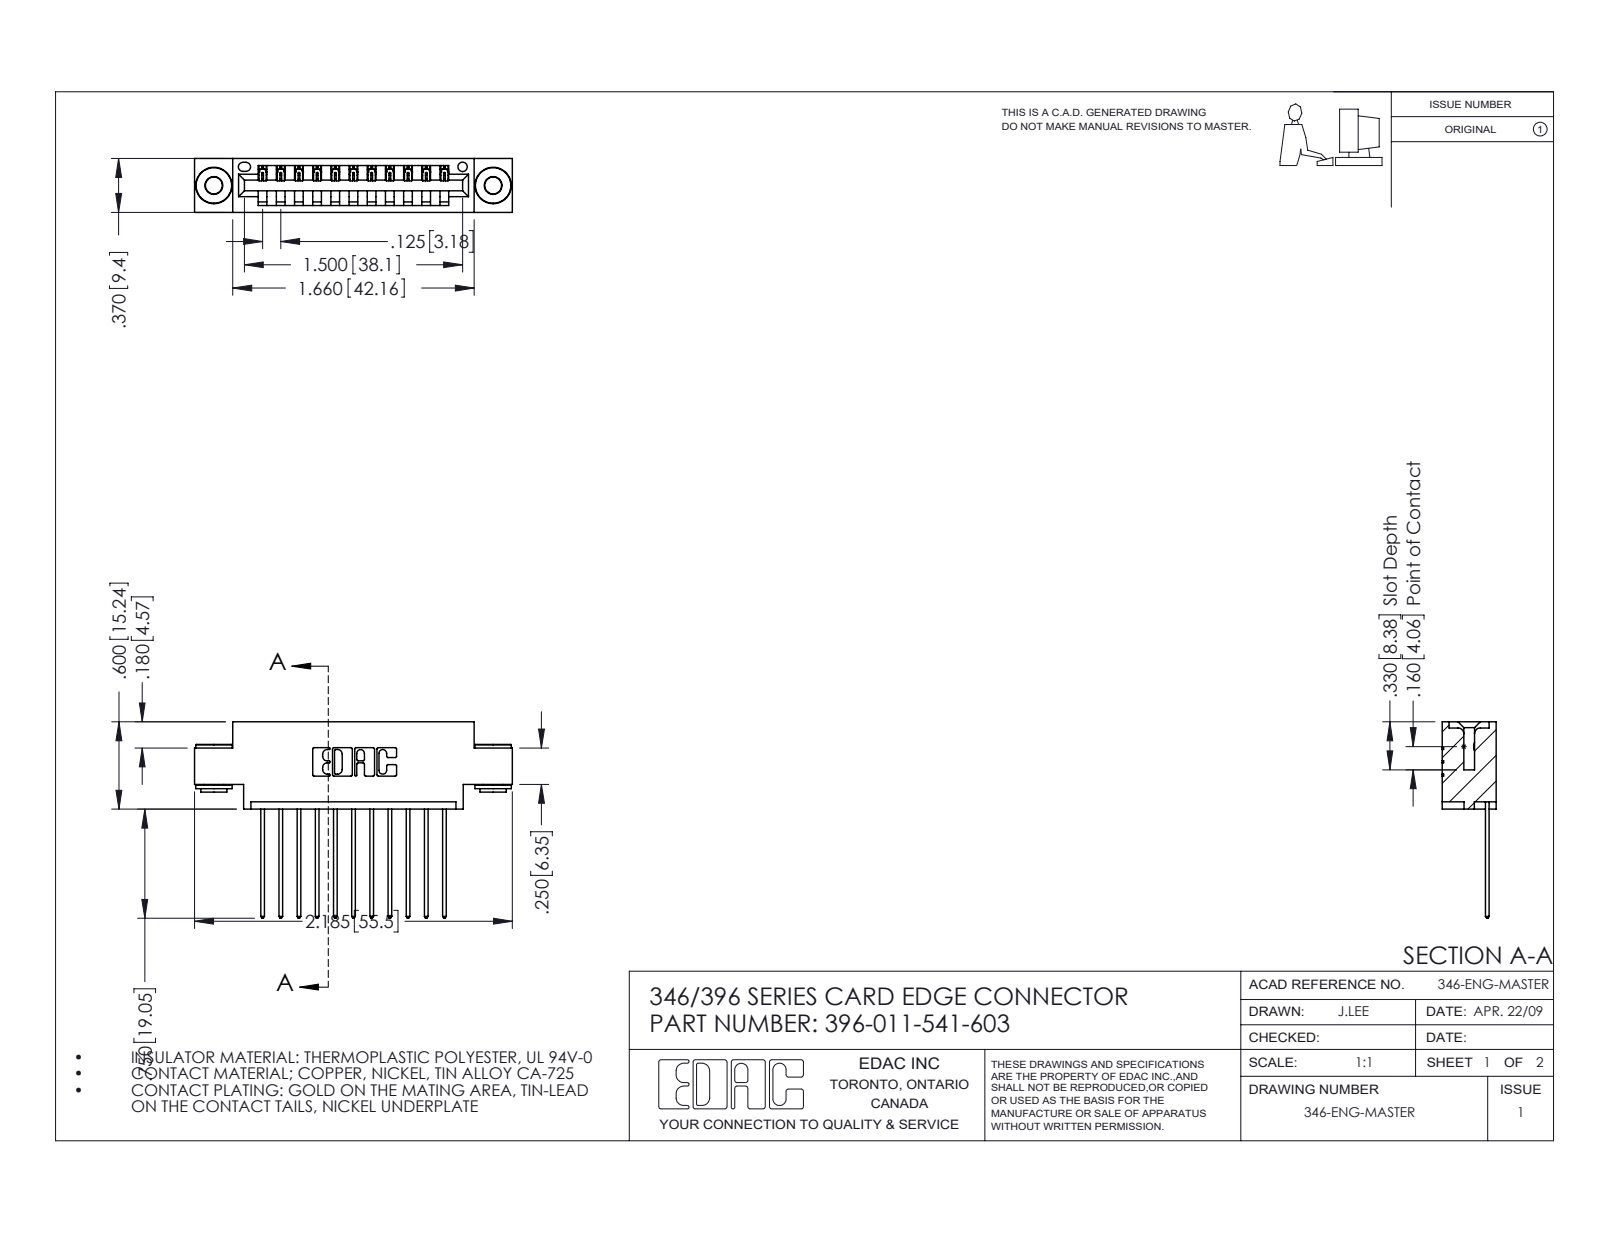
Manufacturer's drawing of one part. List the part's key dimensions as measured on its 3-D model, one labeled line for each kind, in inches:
Part name (STEP PRODUCT): 345-292-001_345-293-141; 396-011-541-603; 345-250-002_345-250-002-102; 346 Part_0.170 Offset - 0.156 Dia-TH
STEP written by: SolidWorks 2016 (CONFIG_CONTROL_DESIGN)
Units: inches
Bodies: 14 solids, 802 faces (530 planar, 264 cylindrical, 8 other)
Overall size (bounding box): 2.185 × 1.35 × 0.37
Volume: 0.305 in³ · Surface area: 10.09 in²
Round holes (diameter × count): ⌀0.116 ×2, ⌀0.156 ×2, ⌀0.064 ×1
Round bosses / shafts (diameter × count): ⌀0.25 ×2, ⌀0.18 ×2, ⌀0.136 ×2
Partial cylindrical surfaces — rounded edges, fillets, slot ends (radius × count): R0.006 ×22, R0.01 ×22, R0.01 ×22, R0.007 ×6, R0.031 ×6, R0.026 ×3, R0.031 ×2, R0.04 ×2
Main face-to-face distances: 0.25, 0.37, 0.048, 0.322, 0.025, 0.072, 0.298, 0.148, 0.222, 0.1
Hole centre spacings: 0.246, 1.715, 1.92
